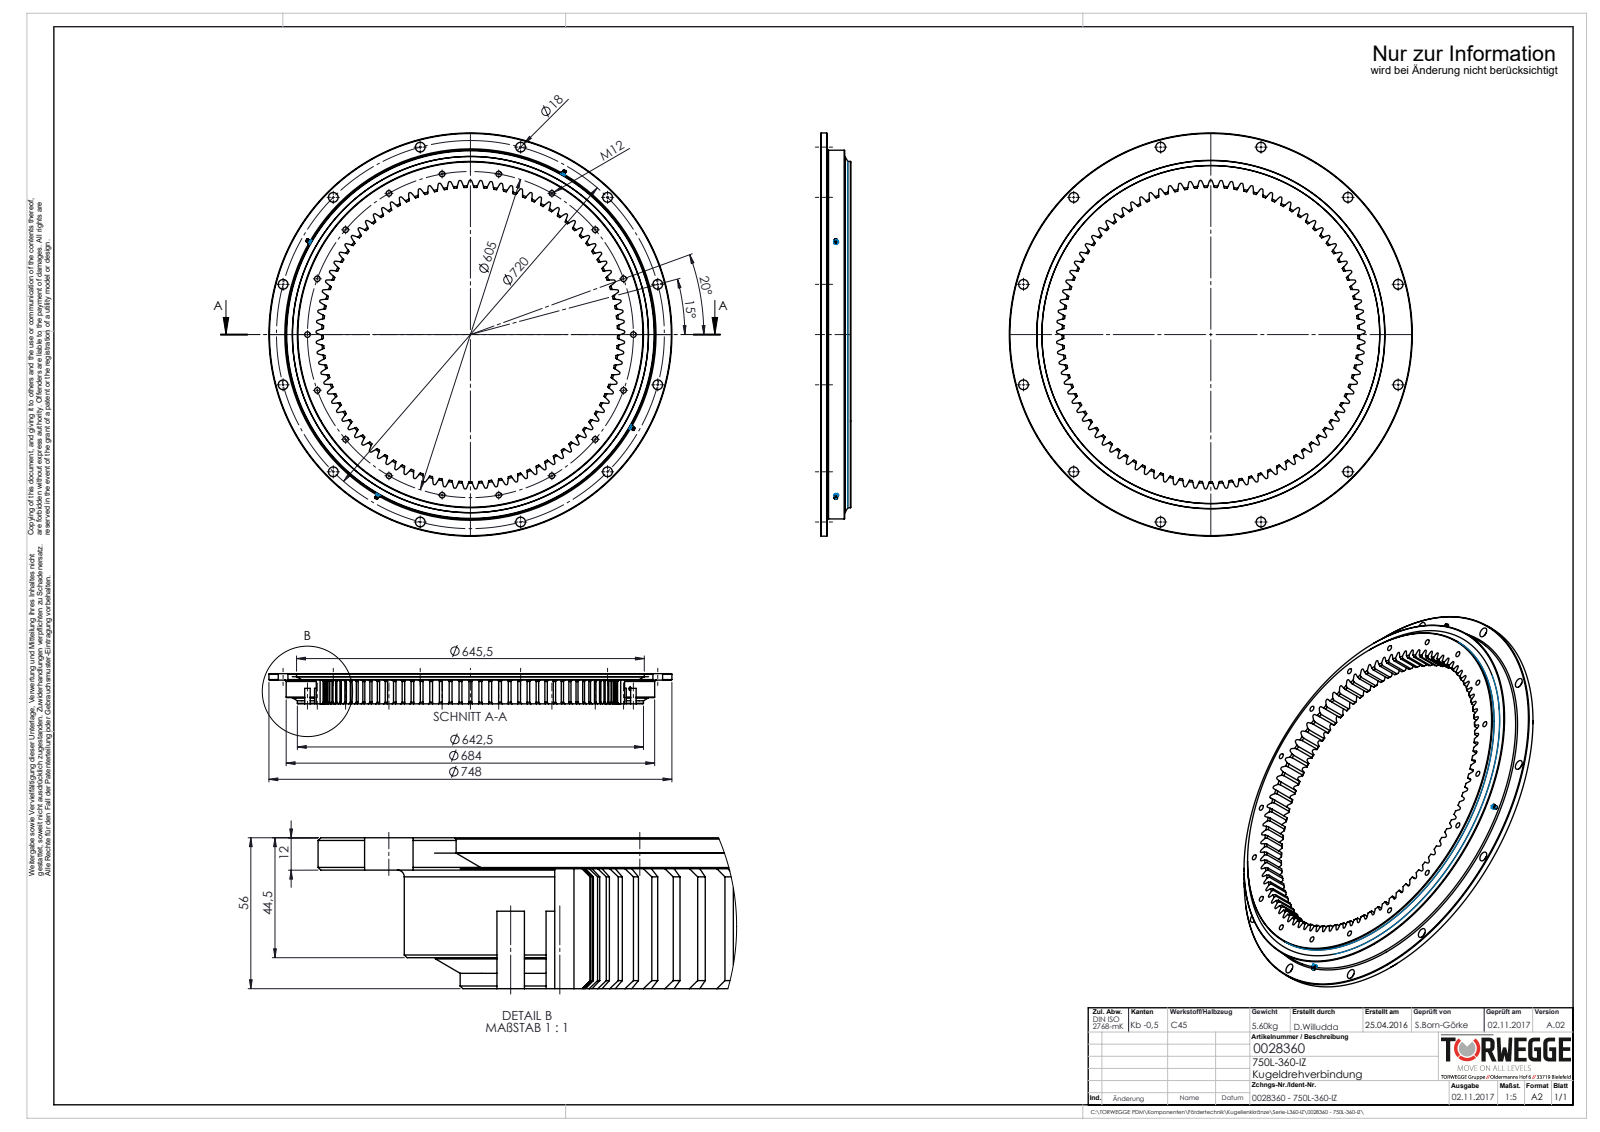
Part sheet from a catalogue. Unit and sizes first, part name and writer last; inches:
Units: inches
Overall size (bounding box): 29.449 × 29.449 × 2.205
Round holes (diameter × count): ⌀0.402 ×18, ⌀0.709 ×12, ⌀25.413 ×1
Round bosses / shafts (diameter × count): ⌀29.449 ×1, ⌀26.929 ×1, ⌀25.295 ×1
Partial cylindrical surfaces — rounded edges, fillets, slot ends (radius × count): R10.748 ×1
Main face-to-face distances: 0.453, 1.752, 2.205, 0.472, 0.02, 1.732, 1.299, 1.28, 0.224, 1.98
Hole centre spacings: 11.909, 14.173, 4.136, 8.146, 22.382, 10.198, 20.628, 20.739
Bodies: 0 solids, 530 faces (27 planar, 162 cylindrical, 341 other)
Part name (STEP PRODUCT): 0028360_750L-360-IZ
STEP written by: SolidWorks 2016 (AUTOMOTIVE_DESIGN)
